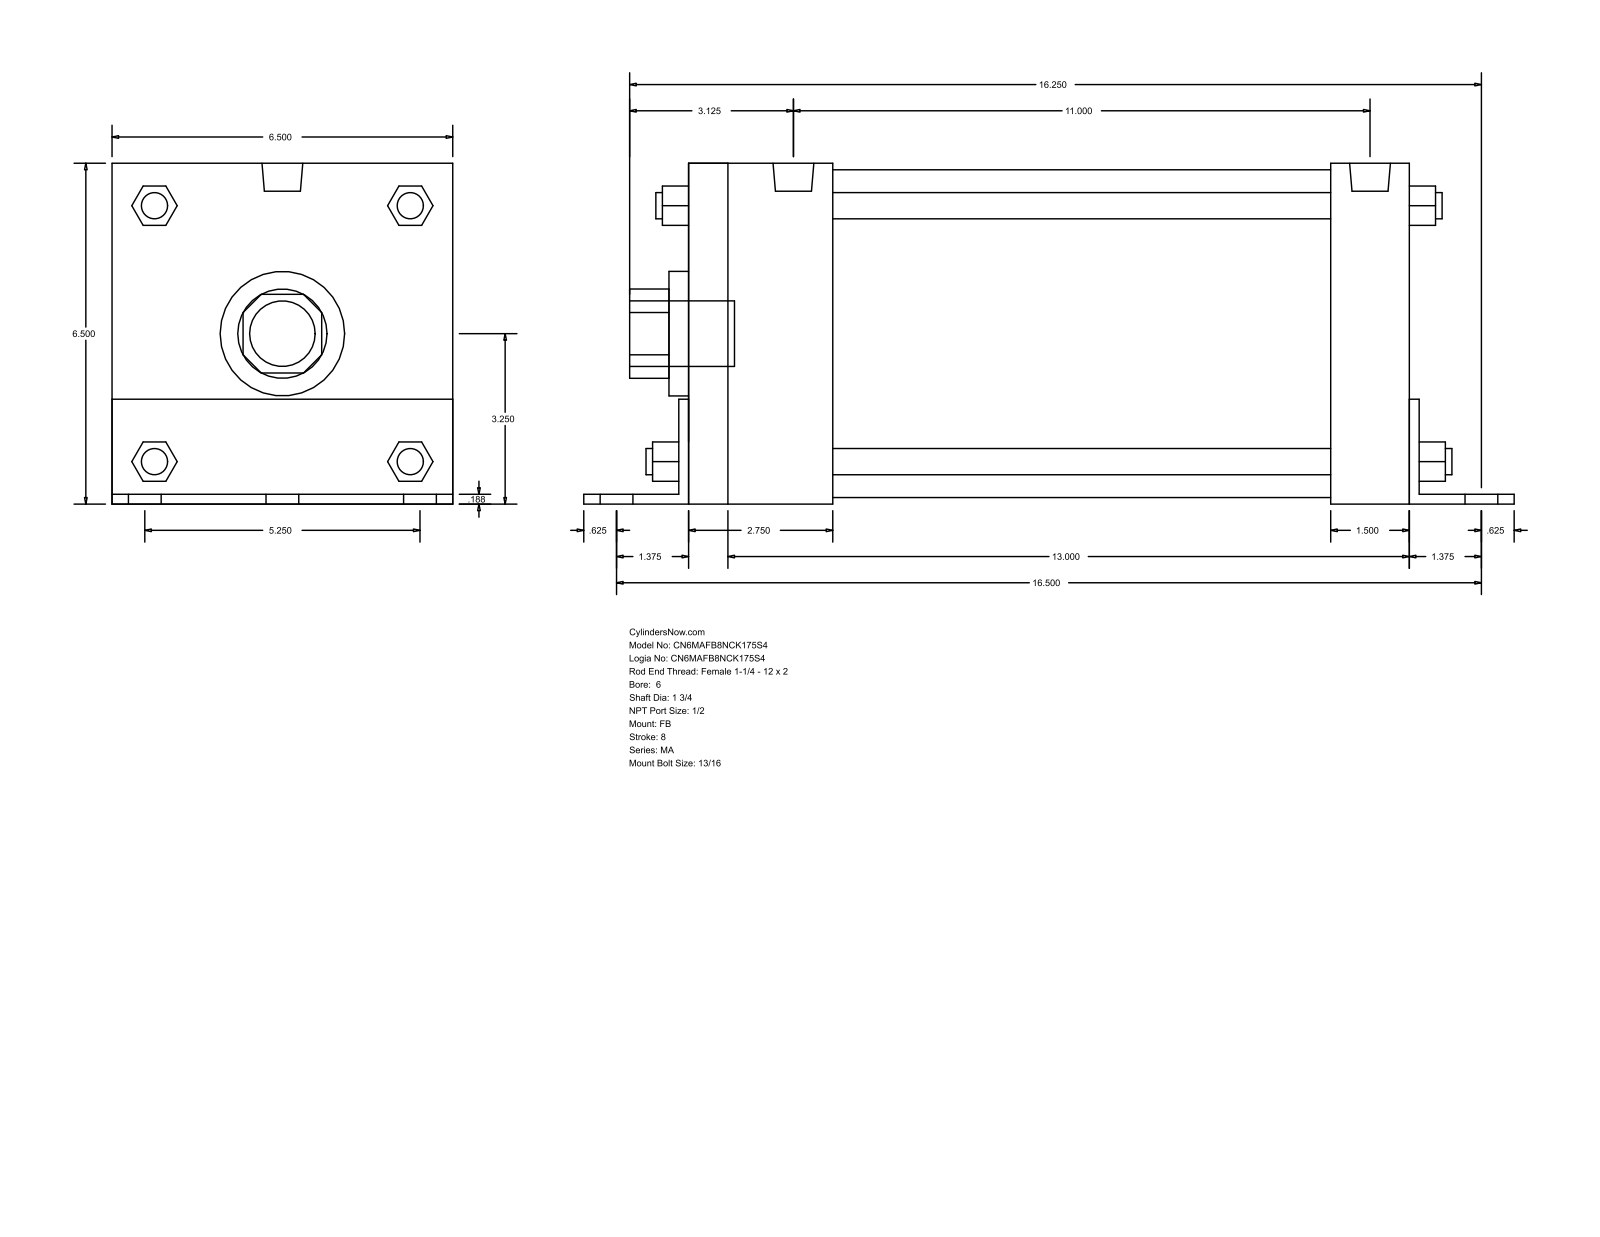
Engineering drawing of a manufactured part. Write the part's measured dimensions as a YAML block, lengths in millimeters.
part_name: "MA_FB__0600_1.75"
step_written_by: "GSSL Pune (CONFIG_CONTROL_DESIGN)"
units: millimeters
bodies: {solids: 0, faces: 140, planar: 105, cylindrical: 35, other: 0}
overall_size: [450.85, 165.15, 165.1]
round_holes:
  - {diameter: 44.45, count: 1}
  - {diameter: 60.33, count: 1}
  - {diameter: 158.75, count: 1}
round_bosses_or_shafts:
  - {diameter: 20.64, count: 6}
  - {diameter: 17.46, count: 4}
  - {diameter: 12.7, count: 4}
  - {diameter: 19.77, count: 2}
  - {diameter: 31.75, count: 1}
partial_cylinders:
  - {radius: 21.63, count: 1}
  - {radius: 32.05, count: 1}
face_to_face_distances: [165.1, 4.76, 349.25, 165.15, 4.71, 160.39, 4.77, 42.86, 354.02, 354.01]
